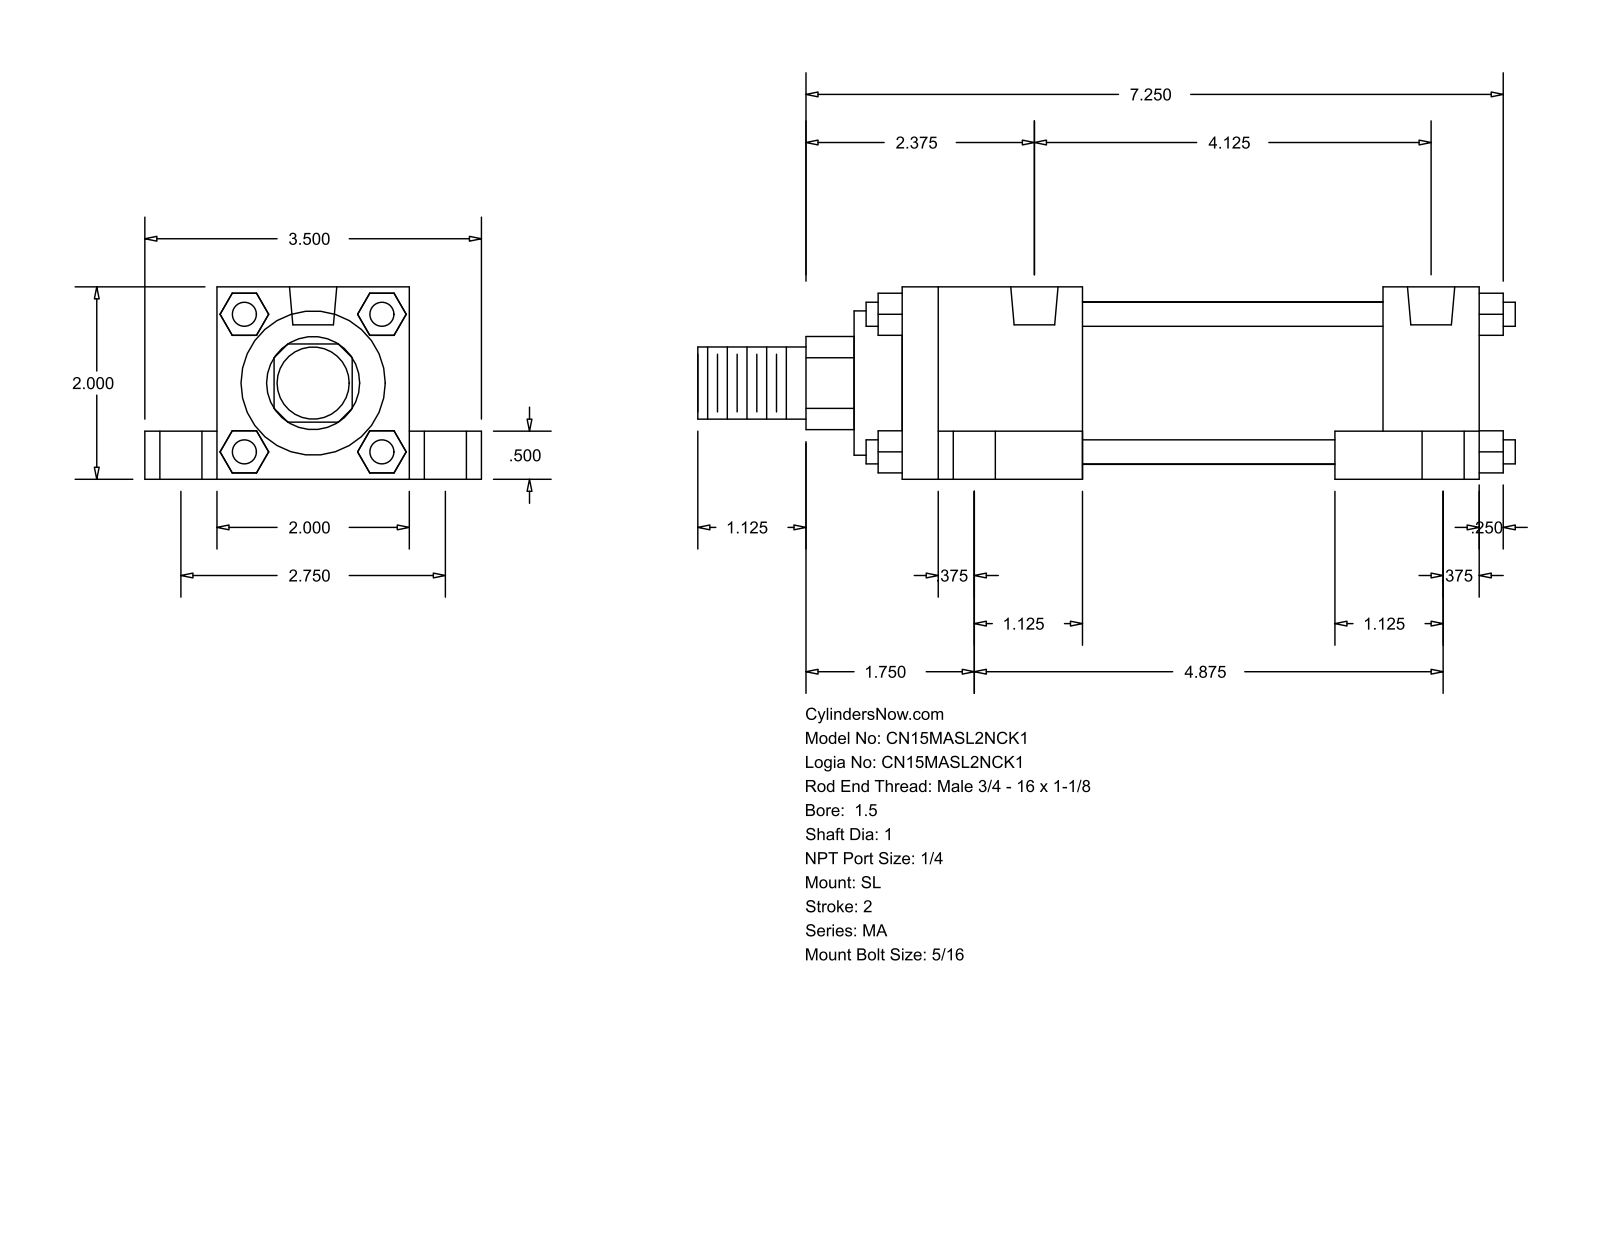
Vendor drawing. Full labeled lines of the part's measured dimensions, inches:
Part name (STEP PRODUCT): MA_SL__0150_1
STEP written by: GSSL Pune (CONFIG_CONTROL_DESIGN)
Units: inches
Bodies: 0 solids, 148 faces (112 planar, 36 cylindrical, 0 other)
Overall size (bounding box): 8.5 × 3.5 × 2
Round holes (diameter × count): ⌀0.313 ×4, ⌀0.437 ×4, ⌀0.687 ×4, ⌀0.492 ×2
Round bosses / shafts (diameter × count): ⌀0.25 ×4, ⌀1.69 ×1, ⌀1.5 ×1, ⌀1 ×1, ⌀0.75 ×1
Partial cylindrical surfaces — rounded edges, fillets, slot ends (radius × count): R0.484 ×1
Main face-to-face distances: 2, 0.5, 0.75, 2.75, 1.5, 0.375, 6, 1, 0.25, 5
Hole centre spacings: 1.38, 1.51, 2.75, 4.125, 4.467, 4.875, 4.945, 5.597
